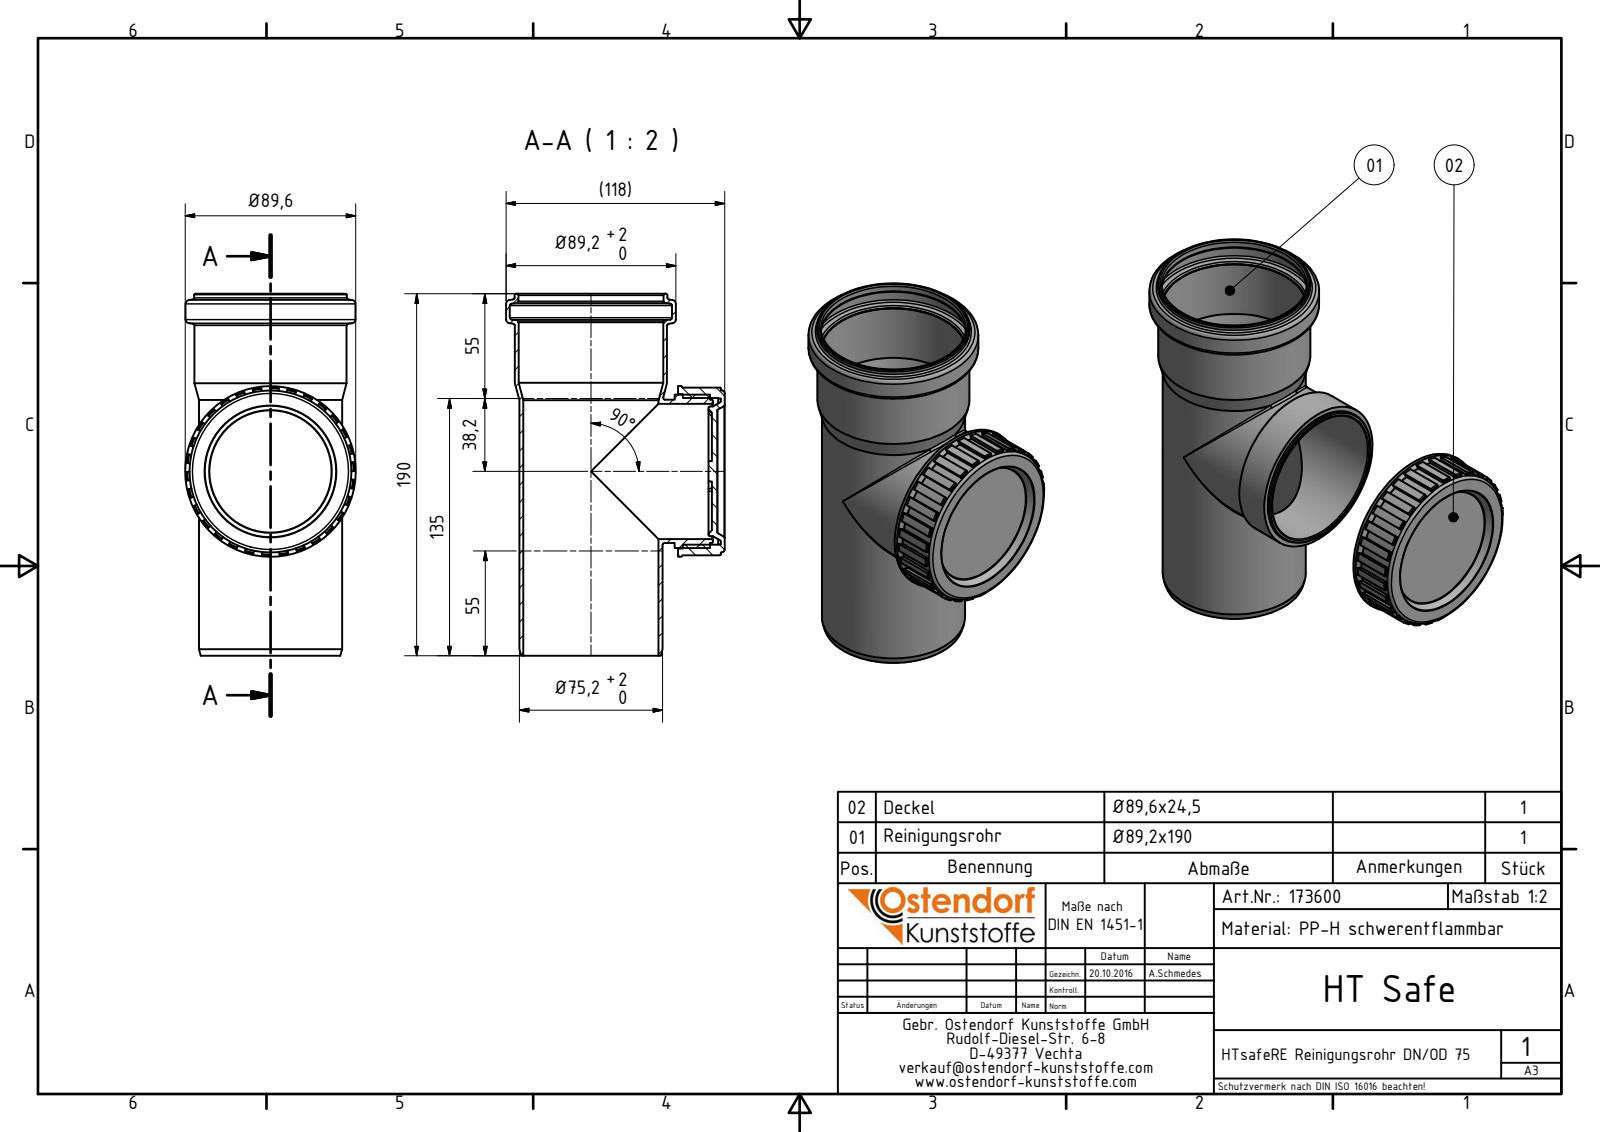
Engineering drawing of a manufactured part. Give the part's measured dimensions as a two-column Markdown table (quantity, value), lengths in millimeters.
| quantity | value |
| --- | --- |
| part name | 113600 HTRE DN_OD 75; 113600 HTRE DN_OD 75 Deckel; 173600 HTsafeRE DN_OD 75 Zusammenbau |
| STEP written by | Autodesk Inventor 2016 (AUTOMOTIVE_DESIGN) |
| units | millimeters |
| bodies | 2 solids, 241 faces (115 planar, 54 cylindrical, 72 other) |
| overall size | 190 × 114.87 × 89.6 |
| volume | 160 674 mm³ |
| surface area | 131 627 mm² |
| round holes (diameter × count) | 71 × 2, 75.9 × 1, 76.2 × 1, 76.6 × 1, 77 × 1, 81 × 1, 85.2 × 1 |
| round bosses / shafts (diameter × count) | 75.2 × 2, 89.6 × 1, 89.2 × 1, 85 × 1, 80.42 × 1, 80.2 × 1, 79.9 × 1, 68 × 1 |
| partial cylindrical surfaces (radius × count) | 1 × 4, 44 × 1 |
| main face-to-face distances | 2.7, 6.7, 4, 17.8, 20.5, 24.5, 2, 4.27, 20, 18.5 |
